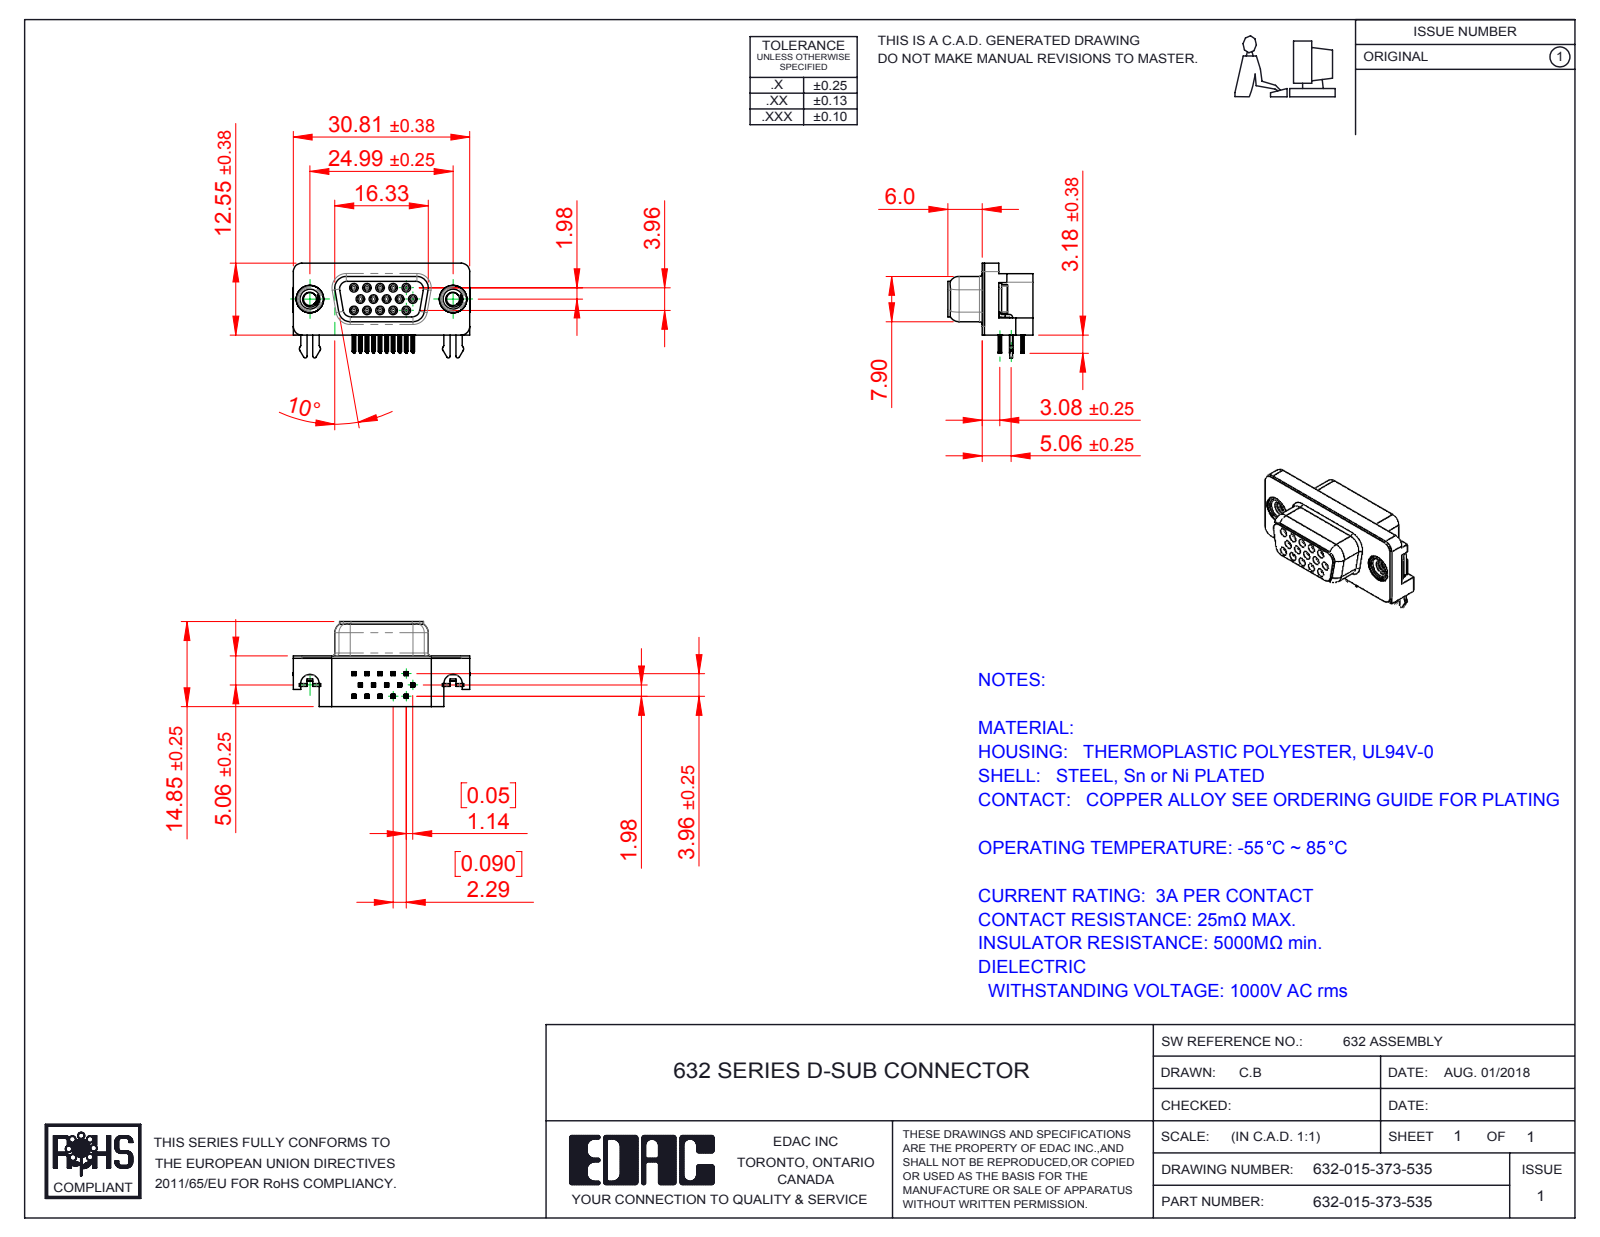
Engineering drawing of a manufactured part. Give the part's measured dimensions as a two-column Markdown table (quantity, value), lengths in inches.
| quantity | value |
| --- | --- |
| part name | 632 Contact Top; 632 M3 Threaded Rivet; 632 Shell_9 Socket; 632 2 Prong Board Lock (+6 more) |
| STEP written by | SolidWorks 2016 (CONFIG_CONTROL_DESIGN) |
| units | inches |
| bodies | 23 solids, 2426 faces (1006 planar, 654 cylindrical, 766 other) |
| overall size | 1.216 × 0.652 × 0.585 |
| volume | 0.183 in³ |
| surface area | 8.275 in² |
| round holes (diameter × count) | 0.031 × 15, 0.035 × 15, 0.089 × 2, 0.098 × 2, 0.157 × 2, 0.189 × 2, 0.197 × 2 |
| round bosses / shafts (diameter × count) | 0.047 × 15, 0.193 × 2, 0.187 × 2, 0.154 × 2 |
| partial cylindrical surfaces (radius × count) | 0.004 × 120, 0.006 × 60, 0.014 × 30, 0.013 × 15, 0.039 × 11, 0.011 × 10, 0.02 × 10, 0.01 × 8 |
| main face-to-face distances | 0.016, 0.333, 0.348, 0.078, 0.114, 0.234, 0.098, 0.252, 0.264, 0.278 |
| hole center spacings | 0.09, 0.09, 0.156, 0.18, 0.238, 0.156, 0.18, 0.27 |
